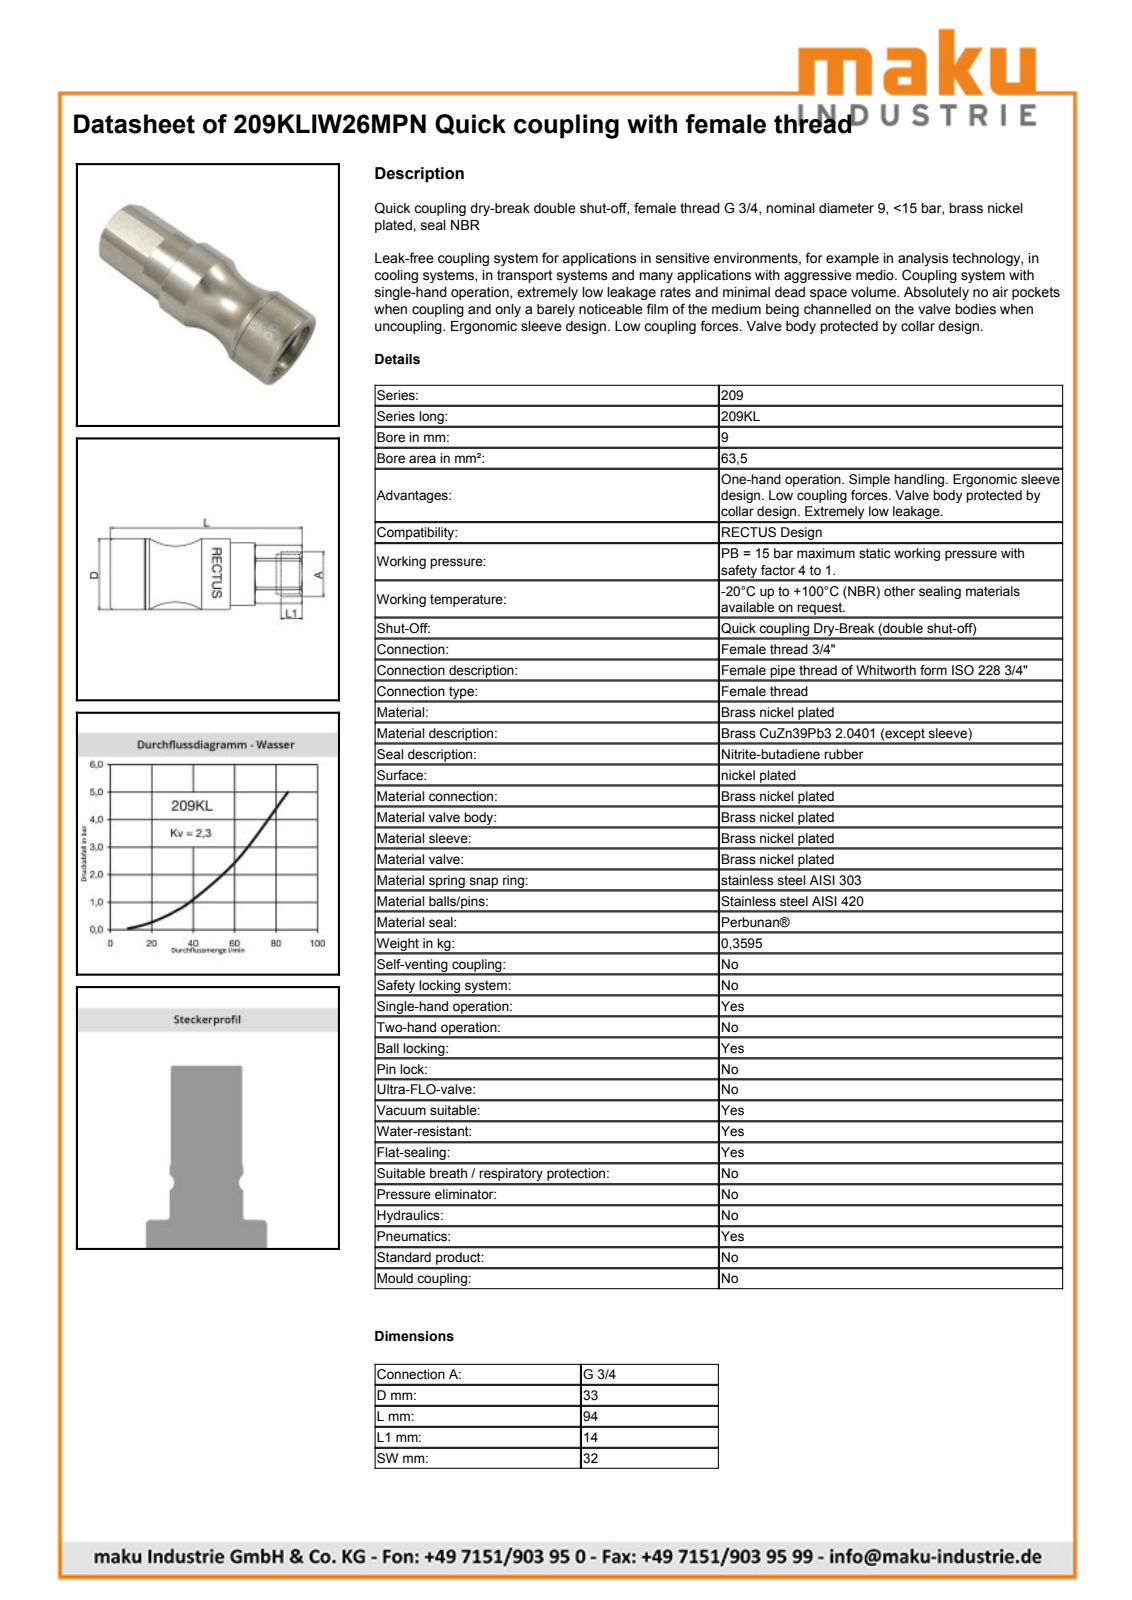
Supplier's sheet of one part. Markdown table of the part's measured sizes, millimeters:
| quantity | value |
| --- | --- |
| part name | D110817 |
| STEP written by | Autodesk Inventor 2013 (AUTOMOTIVE_DESIGN) |
| units | millimeters |
| bodies | 1 solid, 899 faces (304 planar, 121 cylindrical, 474 other) |
| overall size | 94.2 × 35.35 × 35.11 |
| volume | 59 537 mm³ |
| surface area | 23 714 mm² |
| round holes (diameter × count) | 23.6 × 1, 23.65 × 1, 24.1 × 1, 24.12 × 1, 25 × 1, 25.55 × 1, 26.8 × 1, 27.4 × 1, 27.5 × 1, 29.2 × 1, 30.5 × 1, 31.4 × 1 |
| round bosses / shafts (diameter × count) | 33 × 1, 30 × 1, 29 × 1, 26.9 × 1, 25.5 × 1, 23.9 × 1, 23.5 × 1, 21.84 × 1 |
| partial cylindrical surfaces (radius × count) | 16.4 × 1, 18.05 × 1 |
| main face-to-face distances | 32, 78.2, 32.02, 16, 94.2, 1.5, 41.4, 39.1, 66.8, 11.4 |
